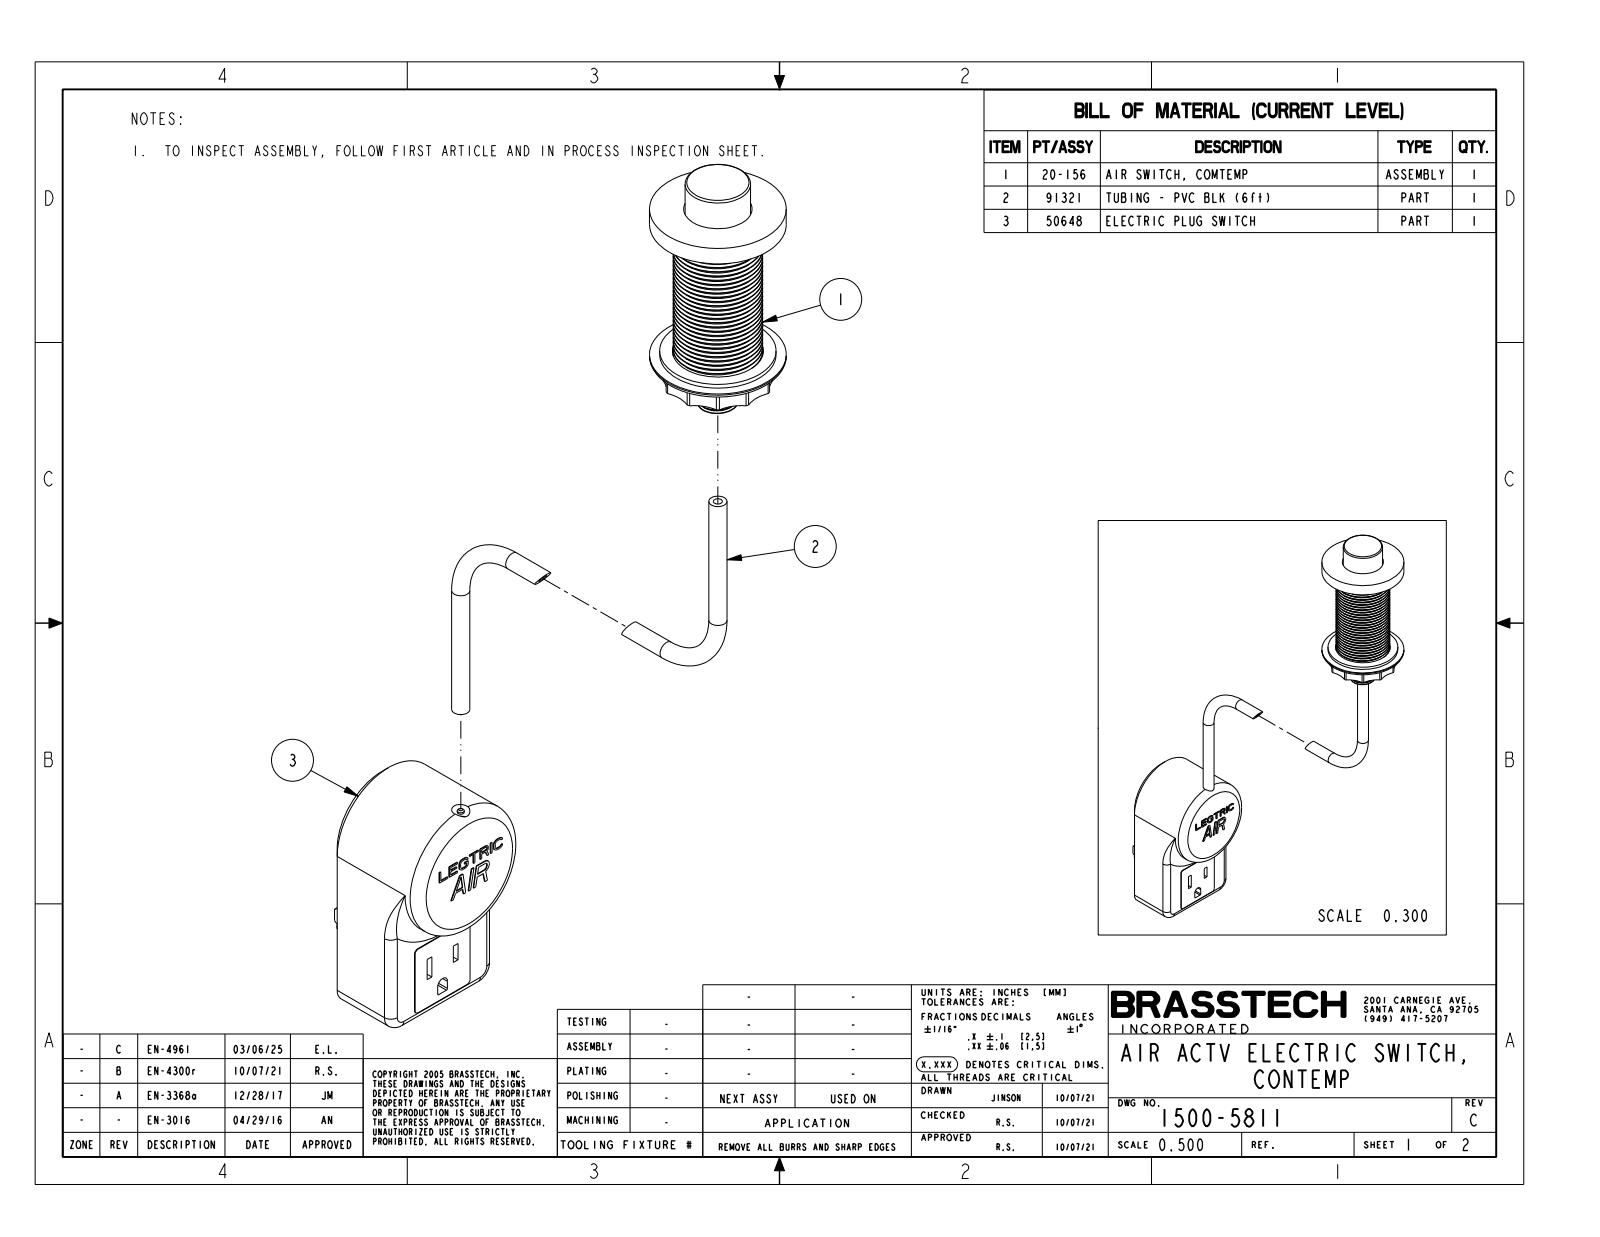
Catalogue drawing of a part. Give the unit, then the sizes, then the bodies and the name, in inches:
Units: inches
Overall size (bounding box): 12.804 × 8.313 × 1.99
Round holes (diameter × count): ⌀0.125 ×4, ⌀0.94 ×1, ⌀1.25 ×1
Round bosses / shafts (diameter × count): ⌀0.25 ×3, ⌀1.99 ×1, ⌀1.88 ×1, ⌀1.6 ×1, ⌀1.23 ×1, ⌀1.135 ×1, ⌀0.9 ×1, ⌀0.557 ×1
Partial cylindrical surfaces — rounded edges, fillets, slot ends (radius × count): R0.5 ×12, R0.06 ×4, R0.125 ×3, R0.02 ×2, R0.25 ×2, R0.095 ×1, R0.81 ×1
Main face-to-face distances: 1.99, 1.7, 0.26, 0.08, 0.36, 12.044, 12.304, 0.52, 1.18, 0.44
Hole centre spacings: 5
Volume: 13.86 in³ · Surface area: 67.69 in²
Bodies: 3 solids, 463 faces (253 planar, 148 cylindrical, 62 other)
Part name (STEP PRODUCT): 1500-5811
STEP written by: CREO PARAMETRIC BY PTC INC, 2018400 (AUTOMOTIVE_DESIGN)
